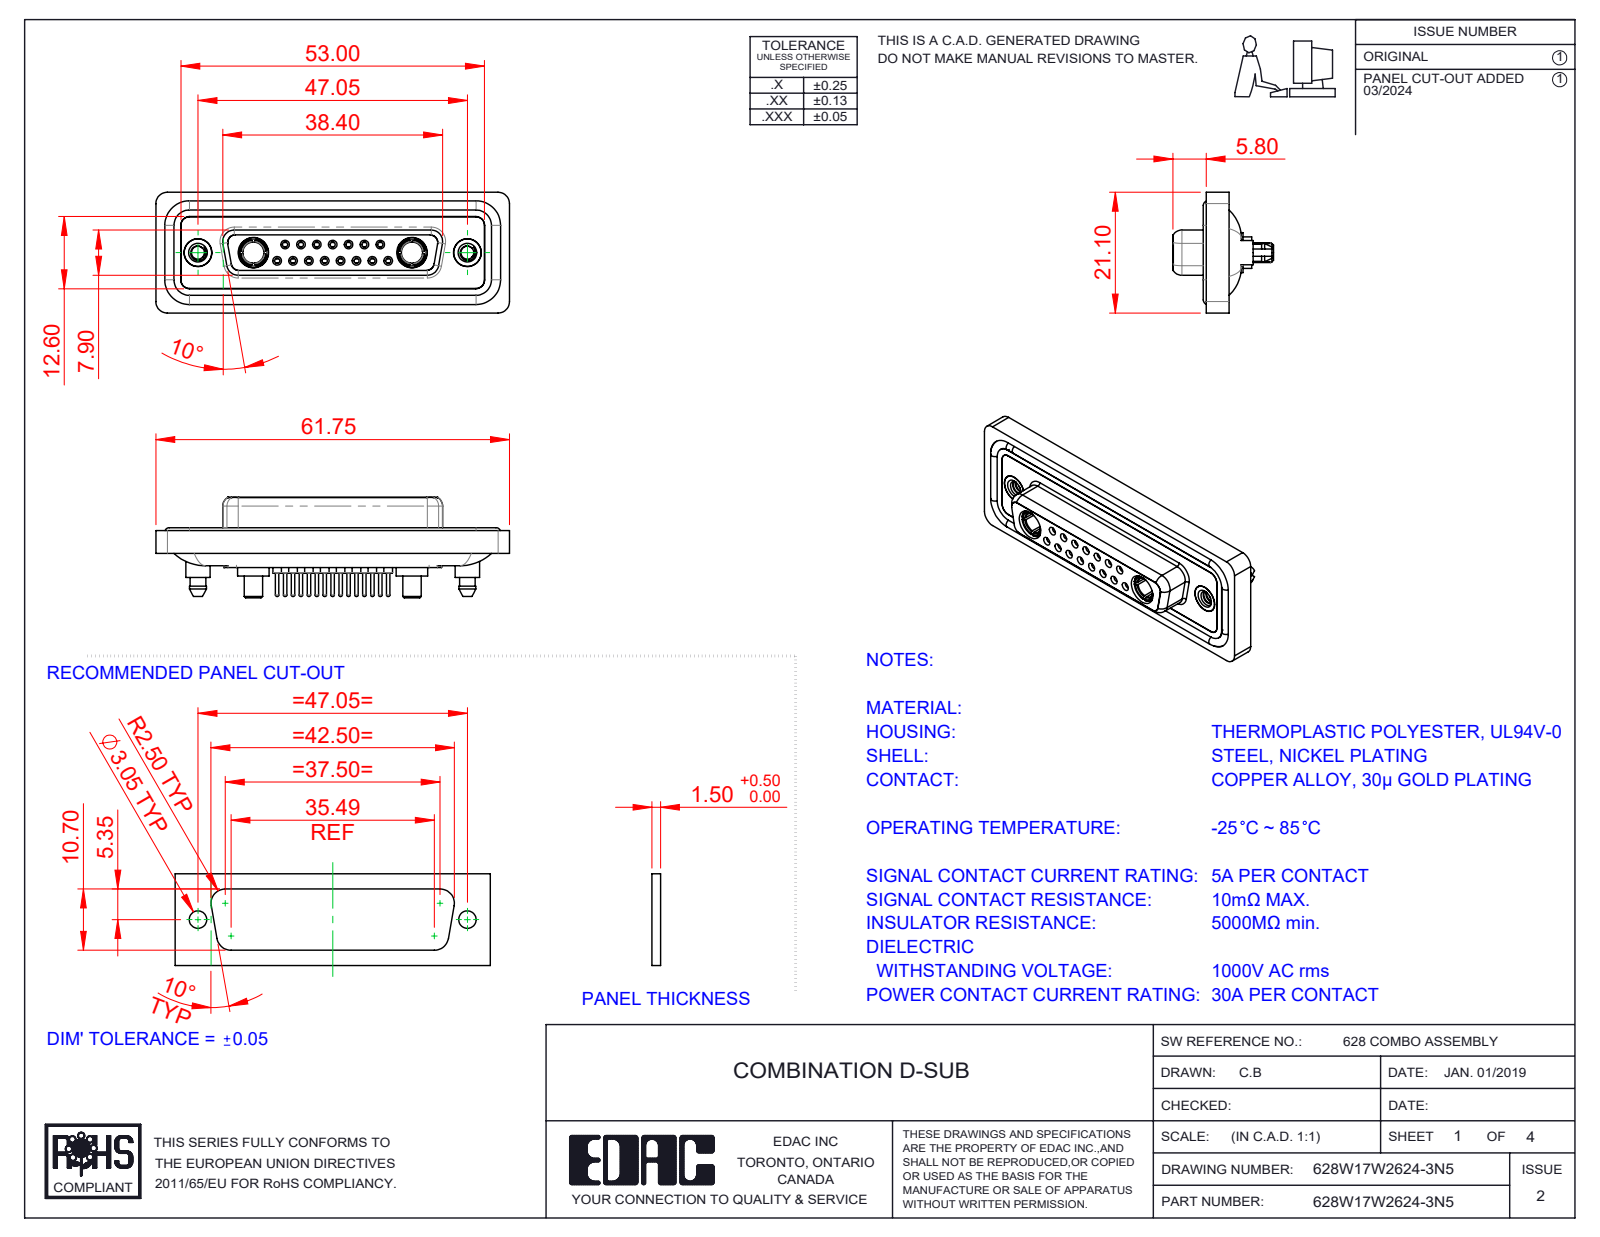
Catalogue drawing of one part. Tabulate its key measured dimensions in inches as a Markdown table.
| quantity | value |
| --- | --- |
| part name | 628Combo Shell Front_25 Contacts; 628Combo Contact Row 2_24; 628Combo Housing_17W2; 628Combo Contact Row 1_24 (+5 more) |
| STEP written by | SolidWorks 2023 (CONFIG_CONTROL_DESIGN) |
| units | inches |
| bodies | 26 solids, 1409 faces (404 planar, 551 cylindrical, 454 other) |
| overall size | 2.431 × 0.831 × 0.691 |
| volume | 0.517 in³ |
| surface area | 22.01 in² |
| round holes (diameter × count) | 0.035 × 15, 0.043 × 15, 0.059 × 15, 0.079 × 15, 0.063 × 8, 0.067 × 7, 0.191 × 4, 0.089 × 2, 0.146 × 2, 0.157 × 2, 0.159 × 2, 0.197 × 2 |
| round bosses / shafts (diameter × count) | 0.087 × 15, 0.024 × 15, 0.063 × 11, 0.217 × 2, 0.213 × 2, 0.205 × 2, 0.195 × 2, 0.195 × 2 |
| partial cylindrical surfaces (radius × count) | 0.059 × 24, 0.079 × 18, 0.063 × 10, 0.053 × 8, 0.01 × 4, 0.02 × 4, 0.024 × 4, 0.026 × 4 |
| main face-to-face distances | 0.016, 0.071, 0.293, 0.222, 0.26, 0.02, 0.278, 0.063, 0.114, 0.043 |
| hole center spacings | 0.124, 0.109, 0.327, 0.218, 0.198, 0.198, 0.295, 0.436 |
